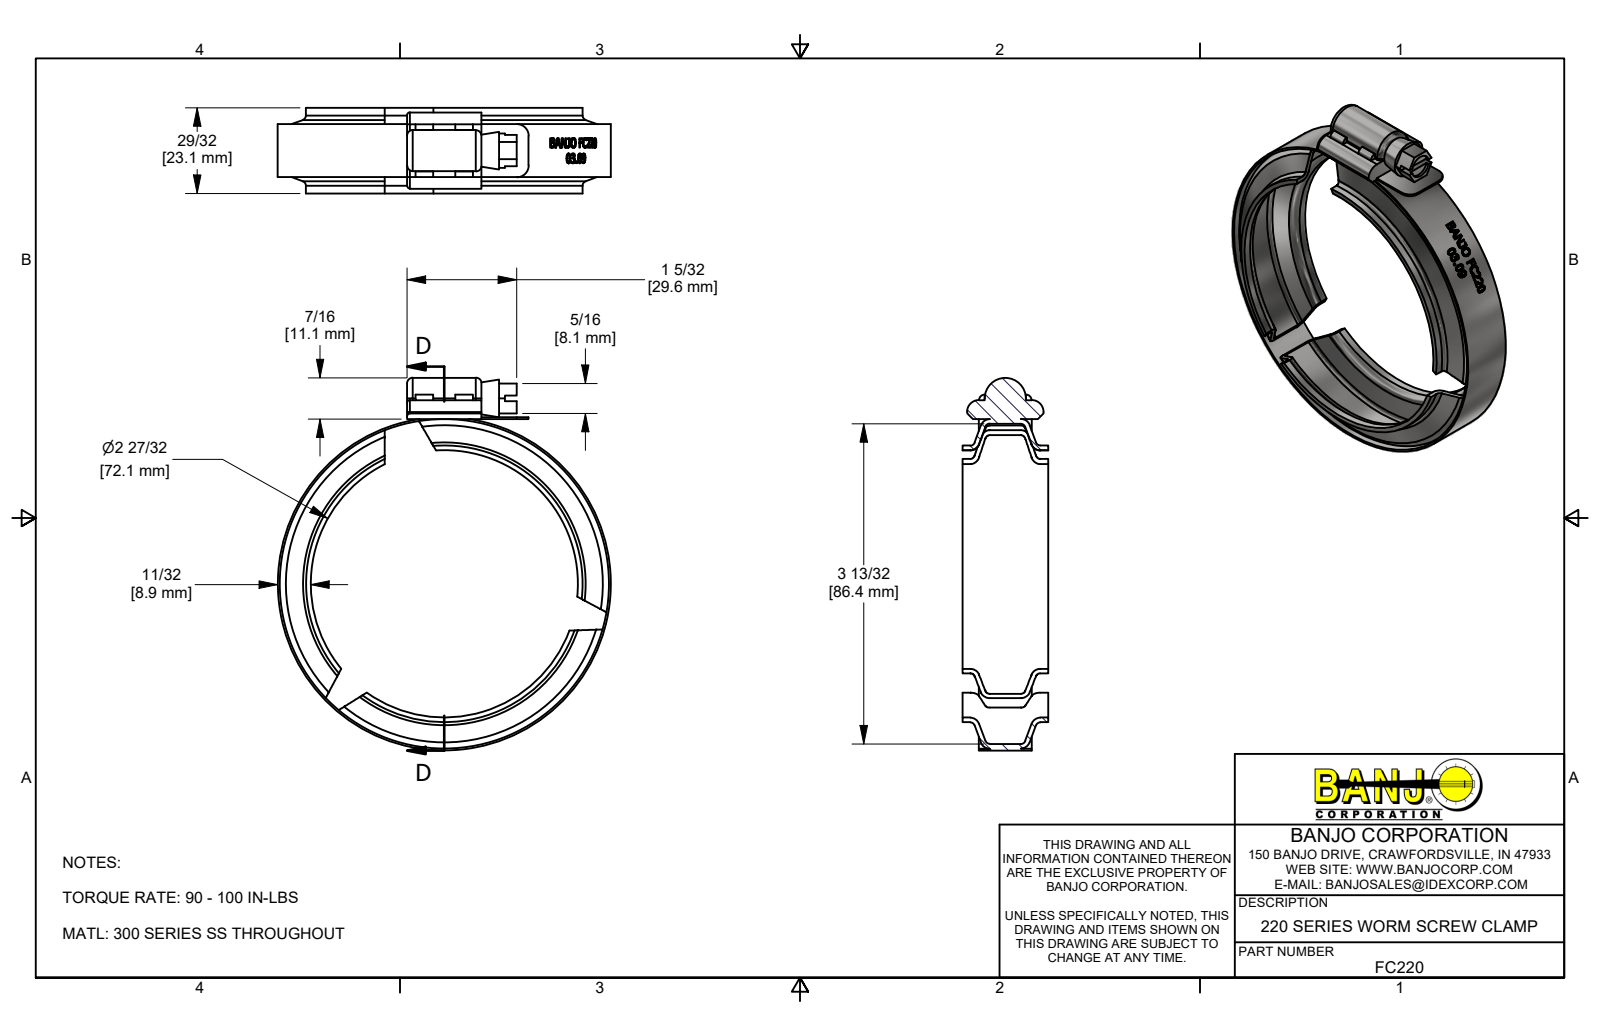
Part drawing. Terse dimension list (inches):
name: FC220
written by: Autodesk Inventor 2018 (AUTOMOTIVE_DESIGN)
unit: in
bodies: 1 solid, 390 faces (137 planar, 57 cylindrical, 196 other)
size: 3.957 × 3.539 × 0.91
volume: 0.911 in³; area: 32.73 in²
holes: 1× ⌀0.25, 1× ⌀2.838, 1× ⌀3.4, 1× ⌀3.5
bosses: 1× ⌀3.539, 1× ⌀2.938
rounds: 4× R0.06, 4× R0.125, 3× R0.03, 1× R0.219, 1× R1.76
face distances: 0.174, 0.737, 0.91, 0.02, 0.563, 0.189, 0.79, 0.317, 0.06, 0.128
